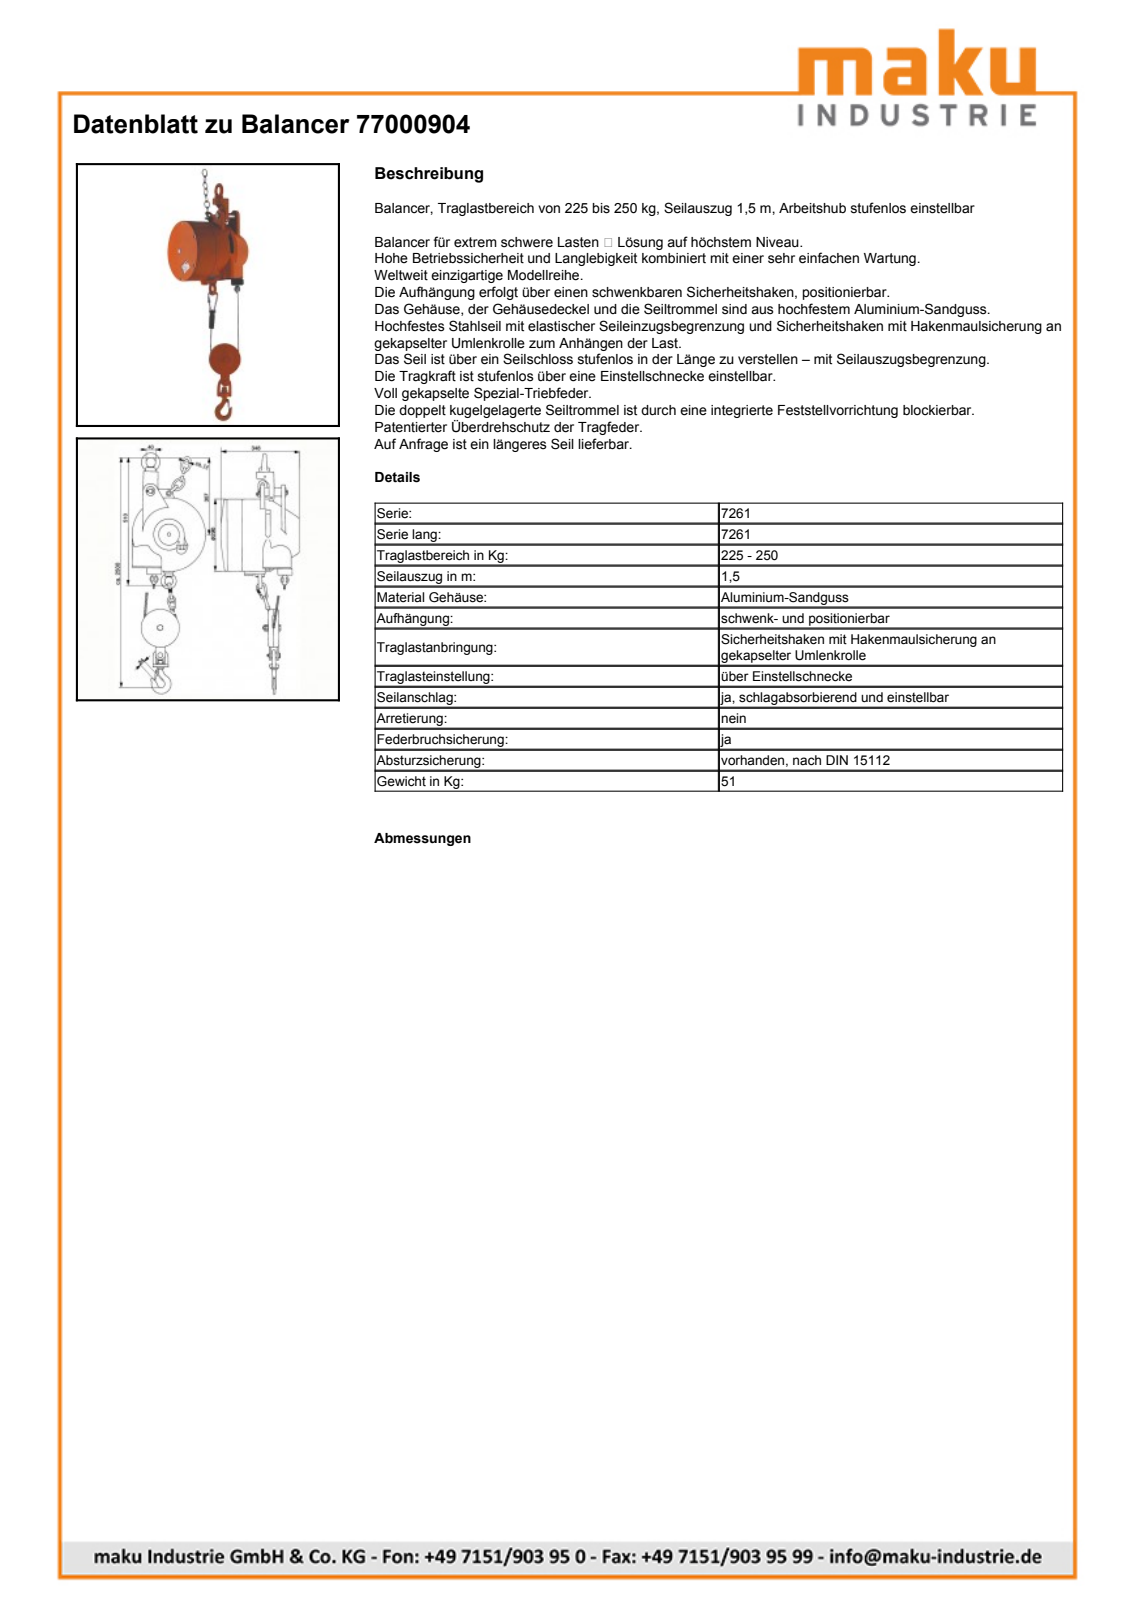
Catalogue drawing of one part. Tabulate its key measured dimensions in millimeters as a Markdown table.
| quantity | value |
| --- | --- |
| part name | 7261; 10000009334_ipt_00013; 10000009334_ipt_00012; 10000009334_ipt_00011 (+8 more) |
| STEP written by | VariCAD 2023-2.04; kernel version (20180118) (AUTOMOTIVE_DESIGN) |
| units | millimeters |
| bodies | 11 solids, 1749 faces (593 planar, 405 cylindrical, 751 other) |
| overall size | 1187.02 × 345 × 292.28 |
| volume | 342 473 mm³ |
| surface area | 633 666 mm² |
| round holes (diameter × count) | 4.2 × 4, 24.05 × 1, 35 × 1 |
| round bosses / shafts (diameter × count) | 5 × 6, 12 × 5, 11 × 5, 15 × 4, 6 × 4, 24 × 3, 21 × 2, 8 × 2 |
| partial cylindrical surfaces (radius × count) | 1.29 × 36, 2 × 35, 1 × 34, 3 × 30, 5 × 19, 6 × 6, 6.25 × 6, 8 × 5 |
| main face-to-face distances | 42, 1, 43, 345, 1.5, 32.5, 8, 89, 44, 10.5 |
| hole center spacings | 49, 364.68, 983.45 |
